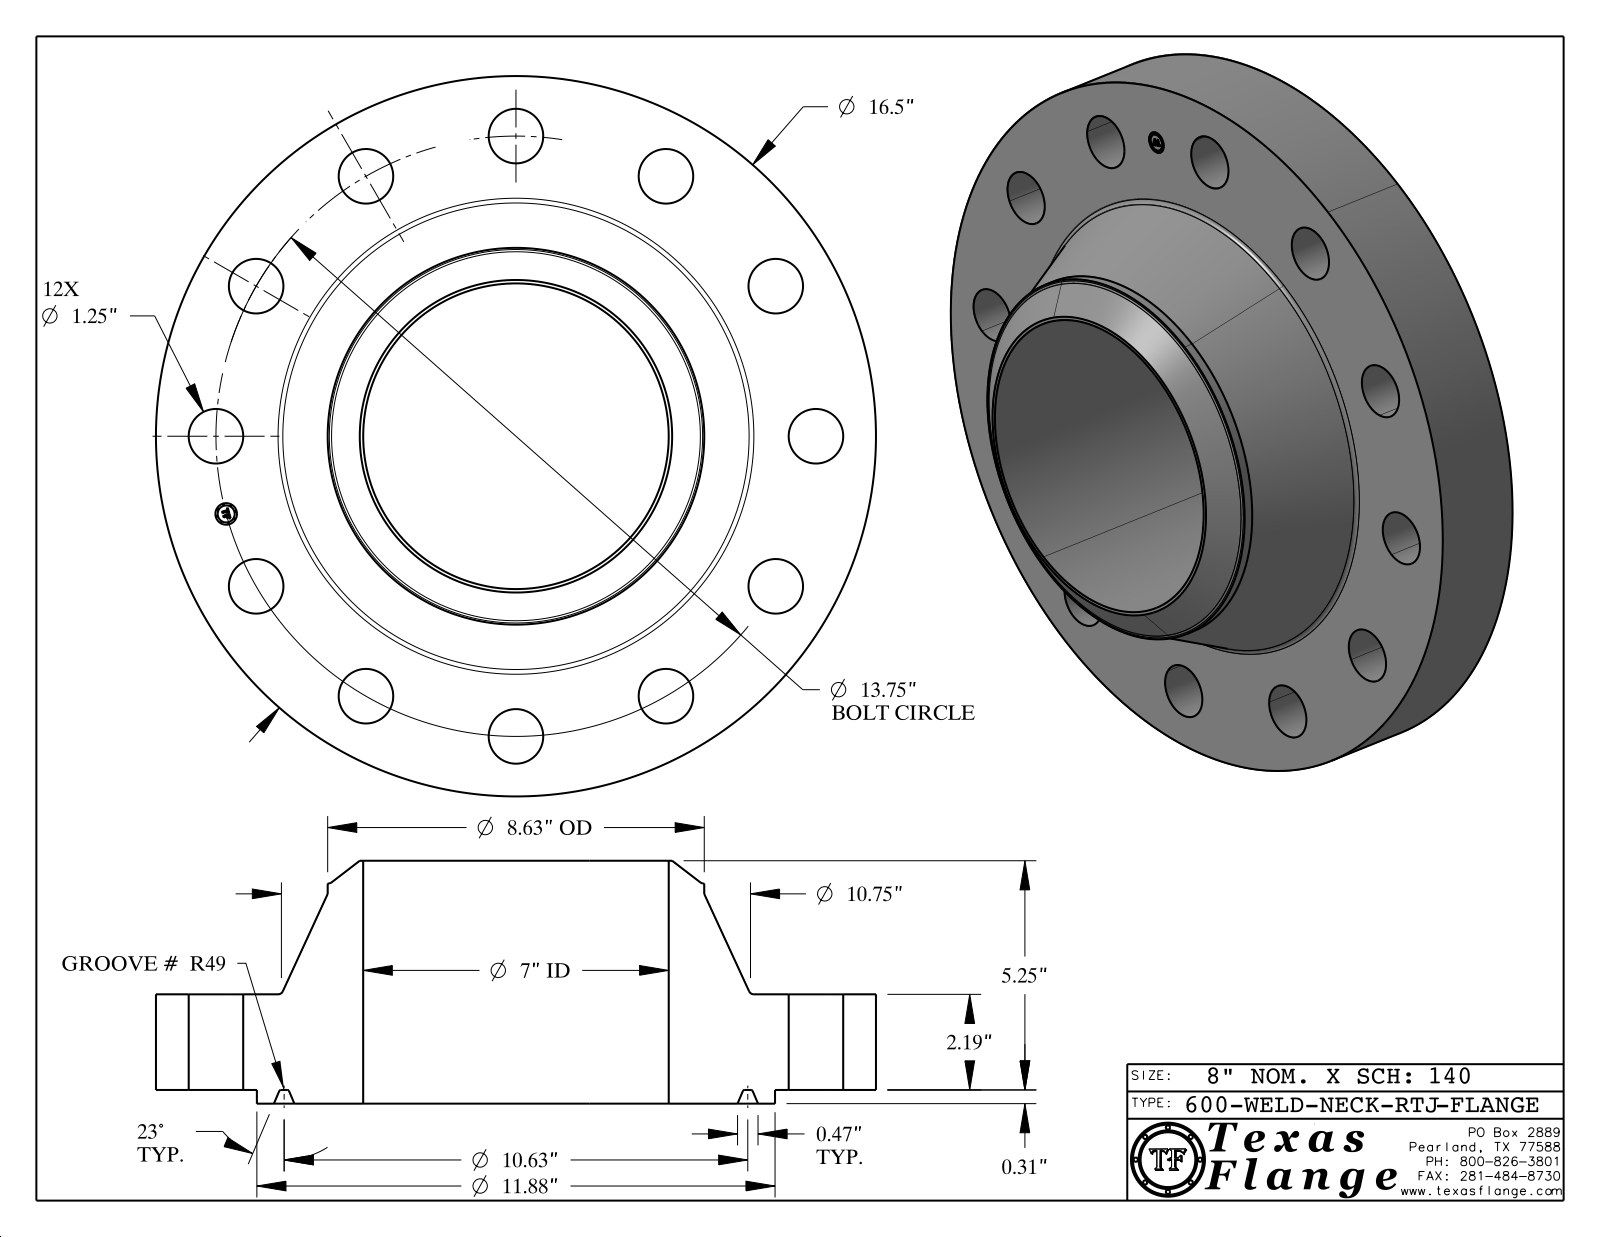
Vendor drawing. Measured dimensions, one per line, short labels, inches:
name: 600-WELD-NECK-RTJ
written by: CATIA V5 STEP AP214 (AUTOMOTIVE_DESIGN)
unit: in
bodies: 1 solid, 441 faces (371 planar, 52 cylindrical, 18 other)
size: 16.5 × 16.5 × 5.563
volume: 462.5 in³; area: 740.5 in²
holes: 12× ⌀1.25, 1× ⌀0.495, 1× ⌀7.001
bosses: 8× ⌀0.03, 1× ⌀16.5, 1× ⌀11.875, 1× ⌀8.63, 1× ⌀0.39
face distances: 2.19, 0.313, 2.503, 5.563, 5.25, 3.06, 2.488, 2.175, 0.015, 3.075
hole spacings: 6.875, 6.875, 9.723, 11.908, 13.281, 3.559, 3.559, 13.75
